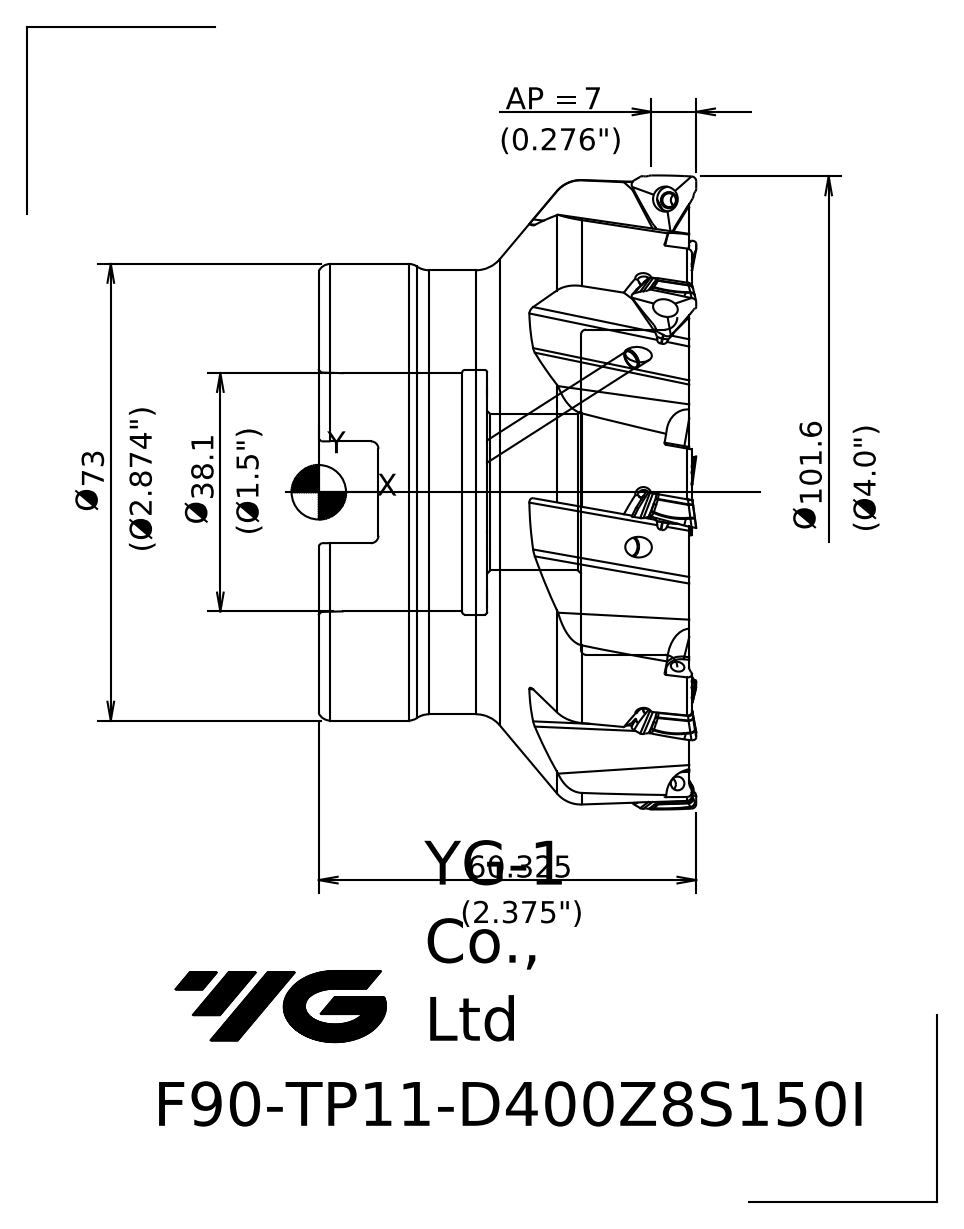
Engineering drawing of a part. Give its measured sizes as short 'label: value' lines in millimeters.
name: 1022B364674Envux
written by: SIEMENS PLM Software NX 10.0 (AP203_CONFIGURATION_CONTROLLED_3D_DESIGN_OF_MECHANICAL_PARTS_AND_ASSEMBLIES_MIM_LF)
unit: mm
bodies: 1 solid, 76 faces (18 planar, 10 cylindrical, 48 other)
size: 101.65 × 101.65 × 60.33
volume: 251 620 mm³; area: 44 282 mm²
holes: 1× ⌀25, 1× ⌀38.1, 1× ⌀39.1, 1× ⌀52
bosses: 1× ⌀73, 1× ⌀71
rounds: 2× R1.2
face distances: 59.23, 17.3, 41.93, 32.3, 15, 26.93, 49.7, 32.4, 17.4, 9.53
